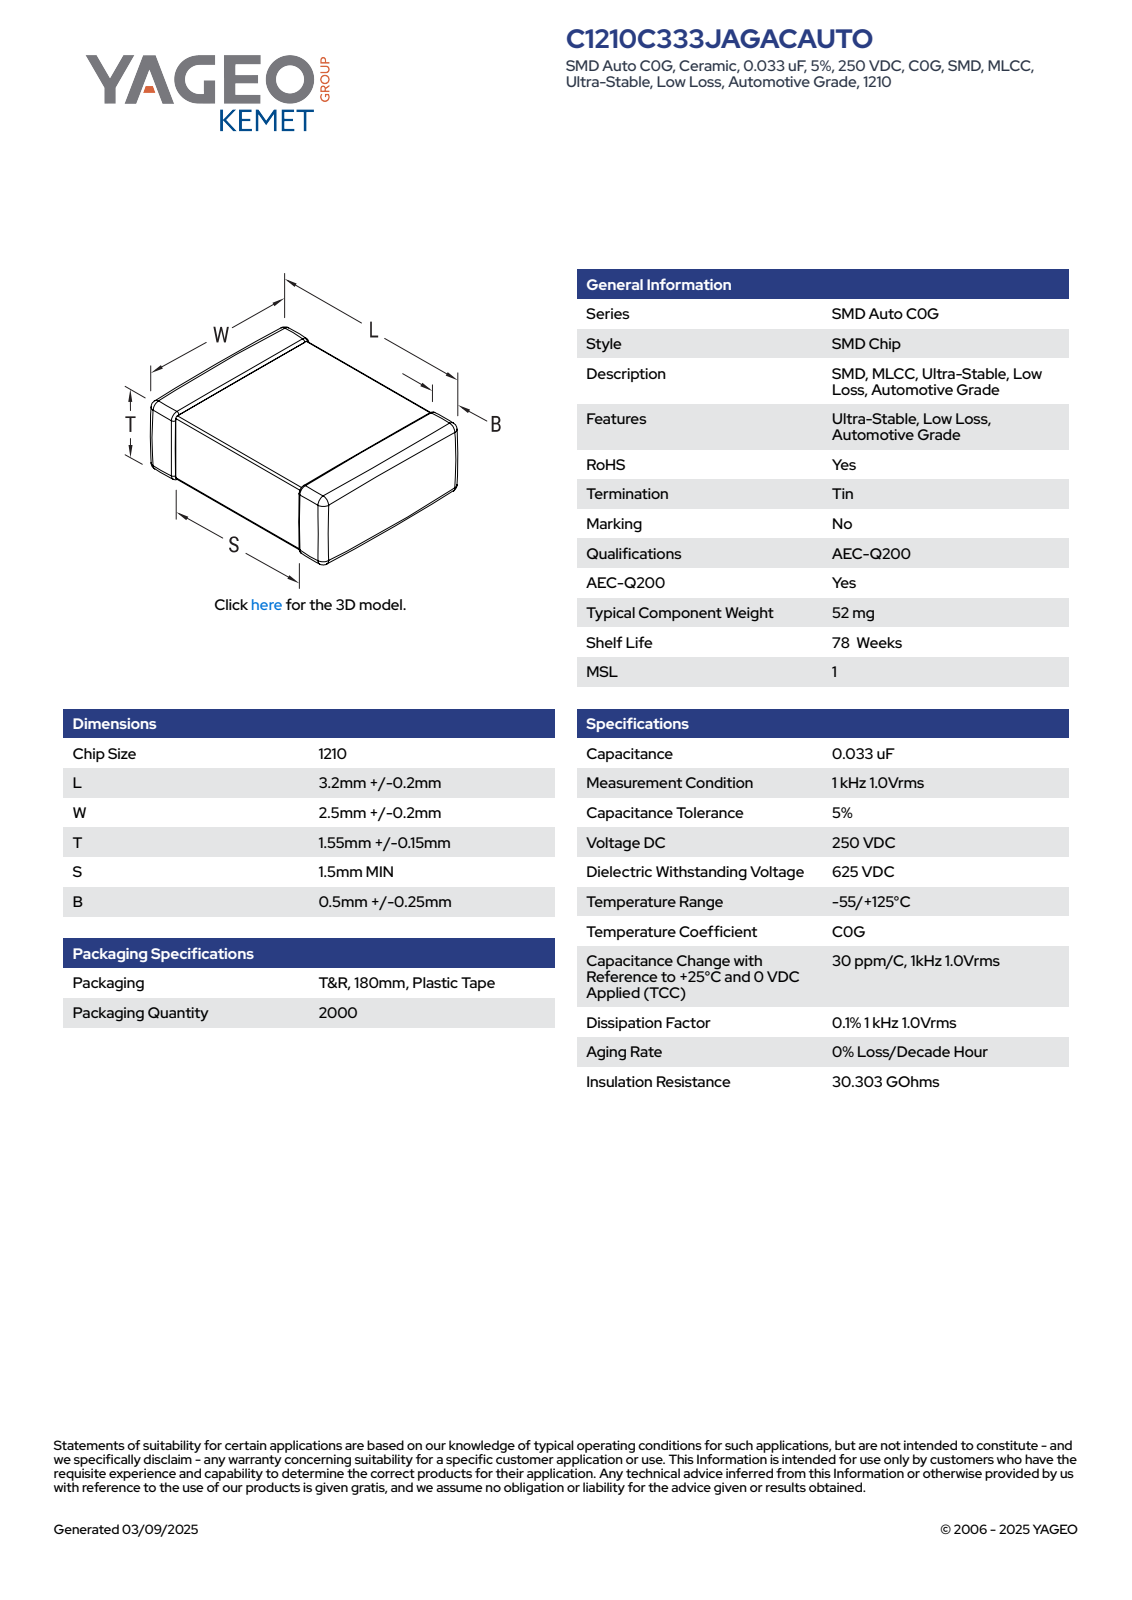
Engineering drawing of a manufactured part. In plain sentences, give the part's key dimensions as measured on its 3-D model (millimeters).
The part is named "CCS_CCSTD_1210_L3.4W2.7T1.7B0.5". Its 3-D file was written by "SolidWorks 2021 (AUTOMOTIVE_DESIGN)". It is 4 solids with 125 faces: 71 planar, 38 cylindrical and 16 other. Overall it measures 3.4 by 2.7 by 1.7 millimeters. Its volume is 15 cubic millimeters and its surface area 39 square millimeters. The main face-to-face distances are 1.64, 1.58, 3.4, 2.64, 1.7, 2.58, 2.7, 1.59, 1.65, 0.4.
